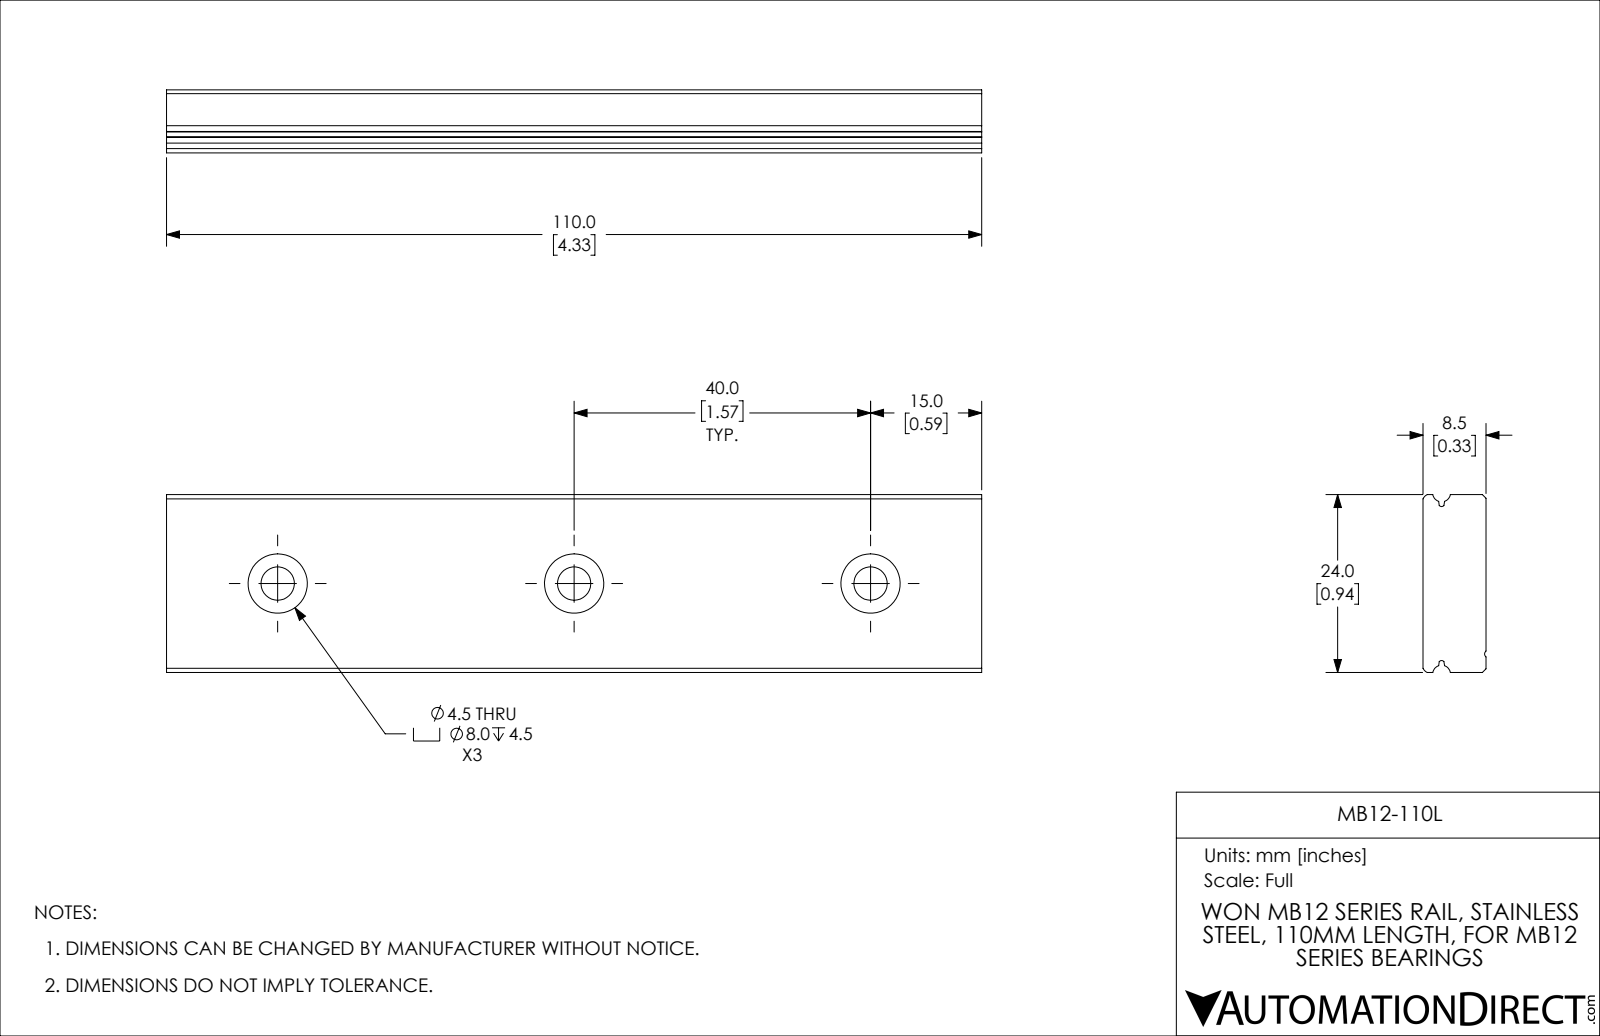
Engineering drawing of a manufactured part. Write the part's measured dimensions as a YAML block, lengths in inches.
part_name: "MB12-110L"
step_written_by: "SolidWorks 2019 (CONFIG_CONTROL_DESIGN)"
units: inches
bodies: {solids: 1, faces: 40, planar: 18, cylindrical: 22, other: 0}
overall_size: [4.331, 0.945, 0.335]
volume: 1.283
surface_area: 12.84
round_holes:
  - {diameter: 0.177, count: 3}
  - {diameter: 0.315, count: 3}
partial_cylinders:
  - {radius: 0.017, count: 2}
  - {radius: 0.045, count: 2}
  - {radius: 0.047, count: 2}
  - {radius: 0.02, count: 1}
face_to_face_distances: [0.335, 0.945, 4.331, 0.087, 0.157, 0.177]
hole_center_spacings: [1.575, 3.15]
